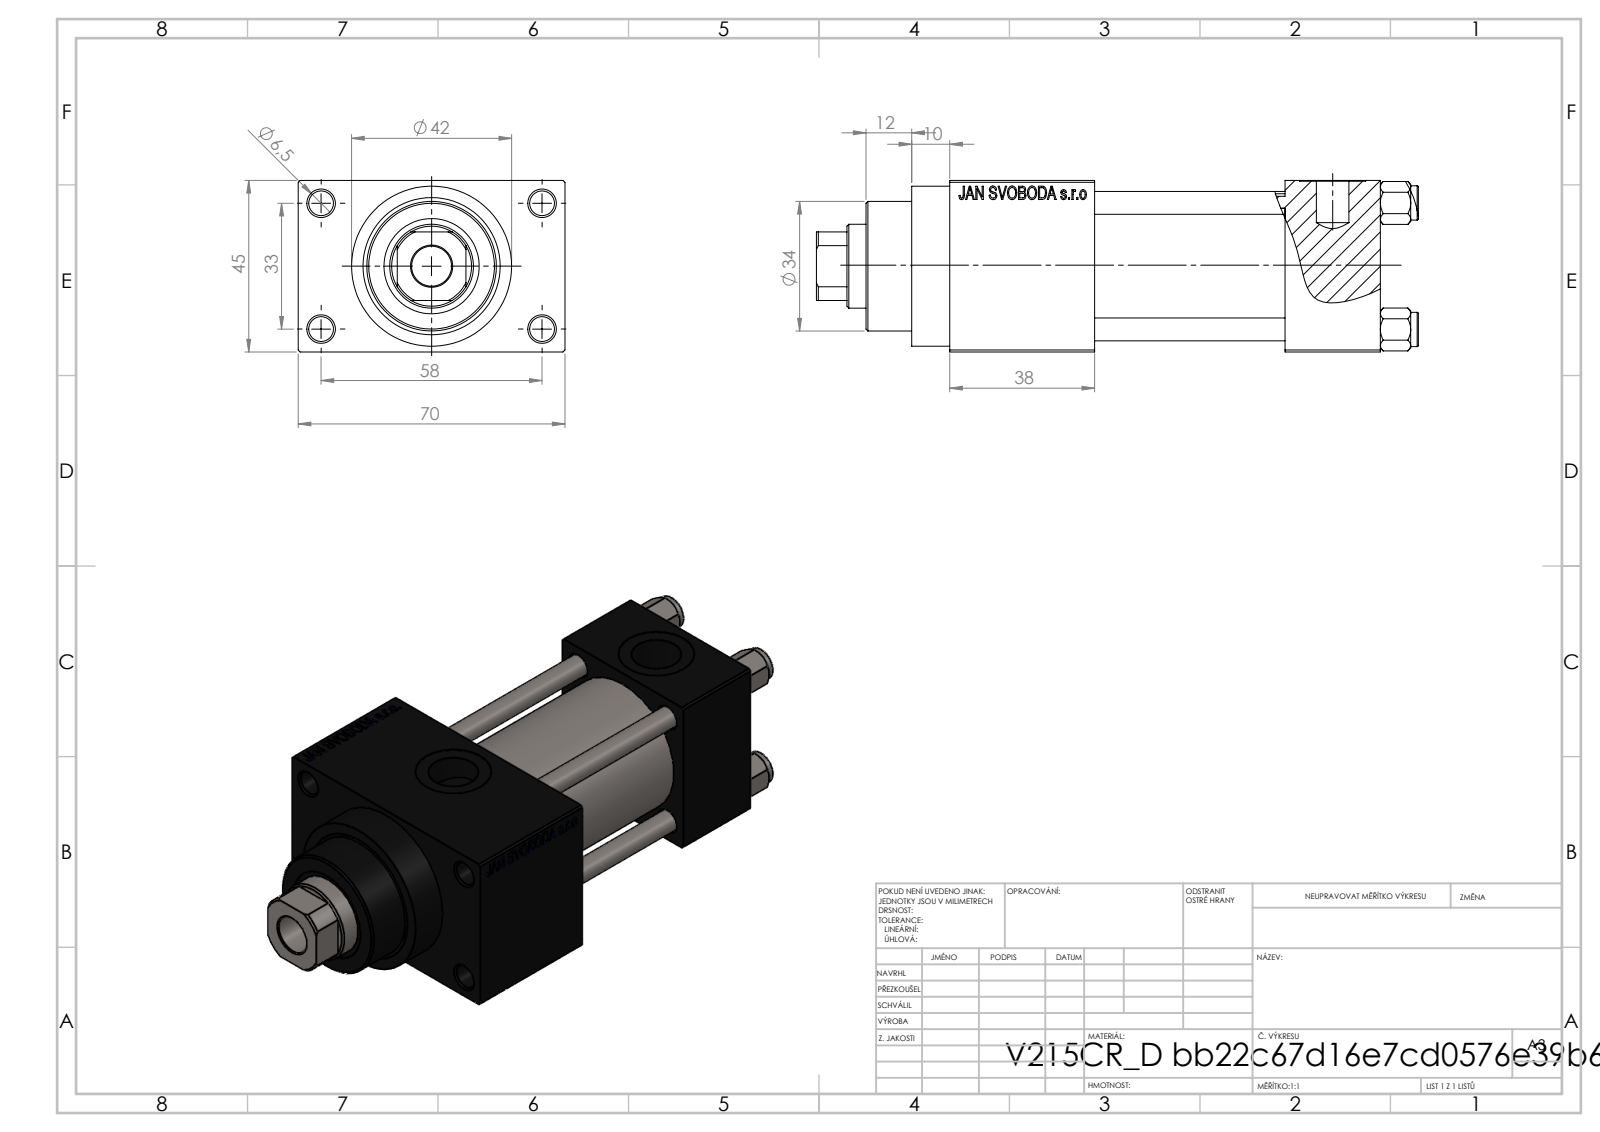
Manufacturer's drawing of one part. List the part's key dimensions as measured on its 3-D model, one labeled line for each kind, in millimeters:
Part name (STEP PRODUCT): NUT_M5_D; V215_VC_A; V215CR_VCP_D; V215CR_D_TYCINKA (+1 more)
STEP written by: SolidWorks 2019 (CONFIG_CONTROL_DESIGN)
Units: millimetres
Bodies: 11 solids, 1105 faces (496 planar, 89 cylindrical, 520 other)
Overall size (bounding box): 158 × 70 × 45
Volume: 244 496 mm³ · Surface area: 79 368 mm²
Round holes (diameter × count): ⌀6 ×4, ⌀6.5 ×4, ⌀7 ×2, ⌀13.16 ×2, ⌀20 ×2, ⌀10.5 ×1, ⌀22 ×1, ⌀24 ×1, ⌀25 ×1, ⌀32 ×1, ⌀33 ×1
Round bosses / shafts (diameter × count): ⌀9 ×4, ⌀42 ×1, ⌀38 ×1, ⌀34 ×1
Partial cylindrical surfaces — rounded edges, fillets, slot ends (radius × count): R10.5 ×1
Main face-to-face distances: 45, 25, 12.5, 57.5, 50, 75, 88, 70, 38, 113
Hole centre spacings: 12.4, 23.48, 33.2, 33.37, 35.35, 45.6, 56.35, 33
